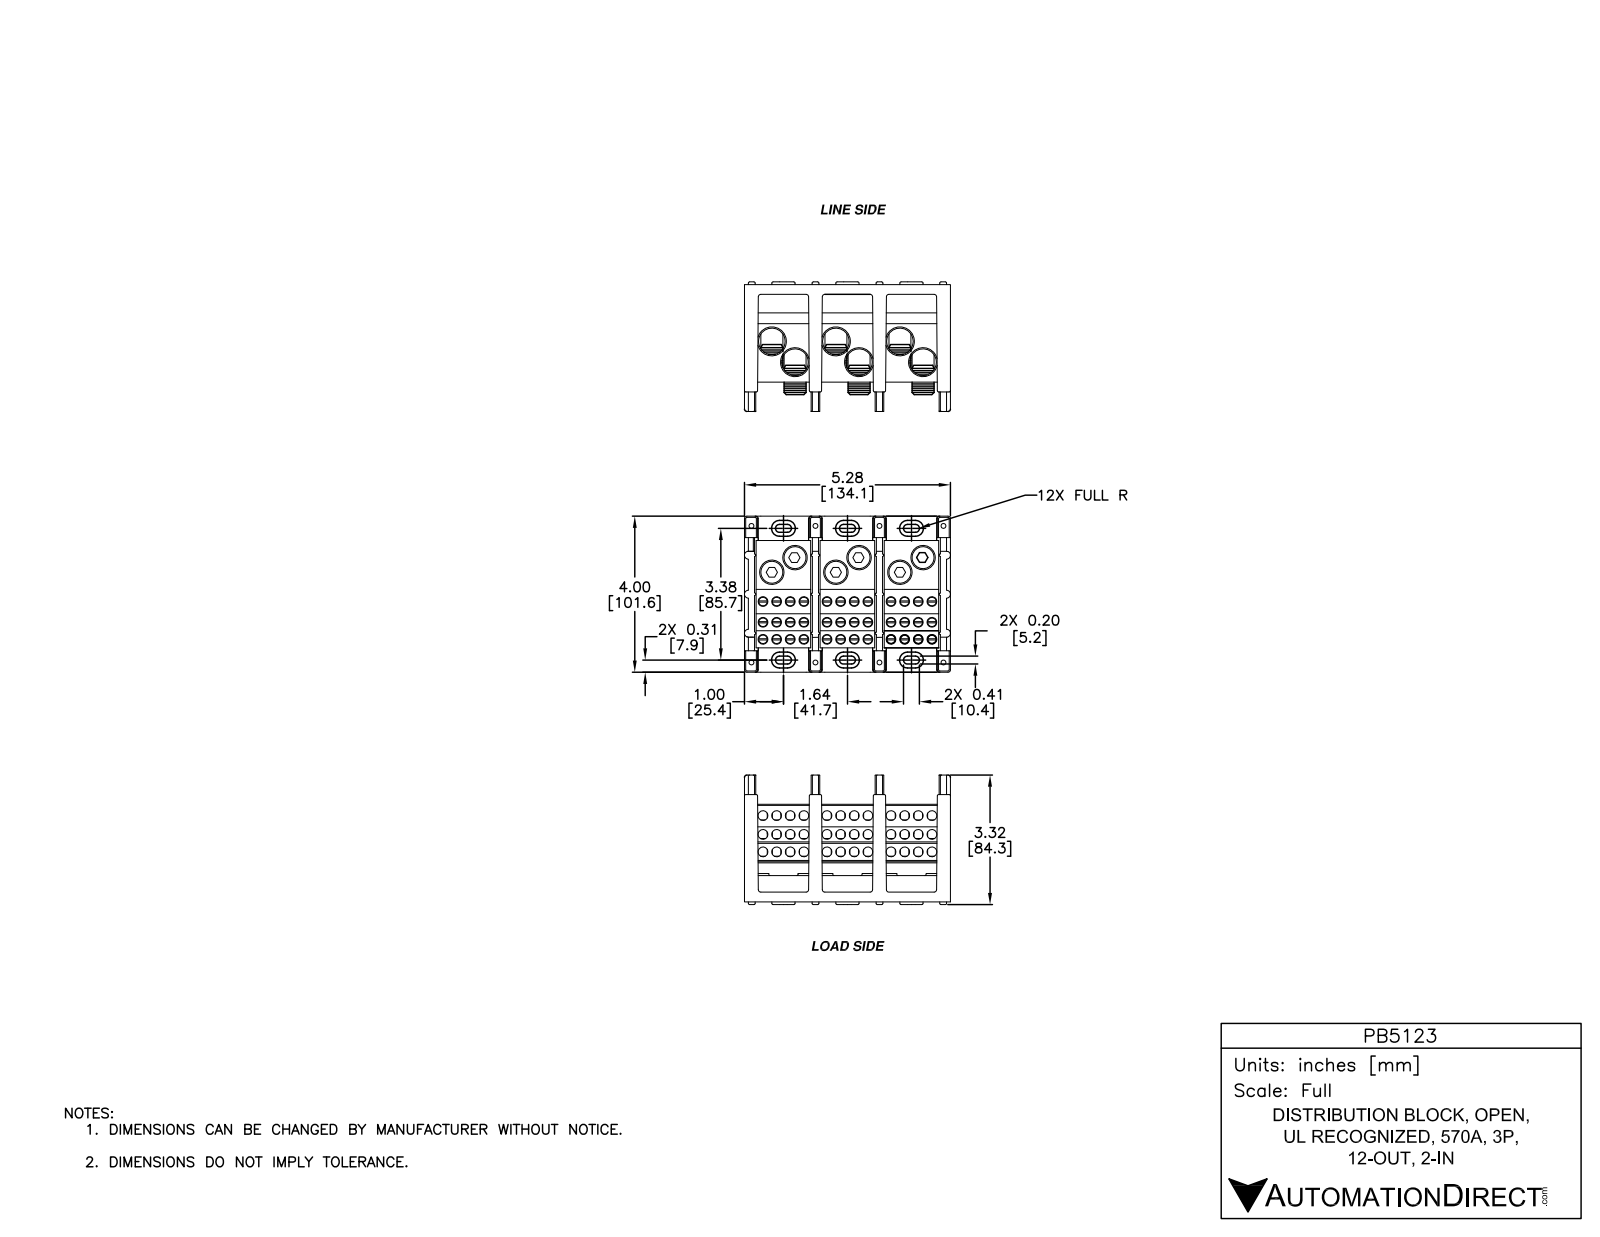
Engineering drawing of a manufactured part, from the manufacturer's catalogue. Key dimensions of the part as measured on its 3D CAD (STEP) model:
Part name (STEP PRODUCT): PB5123
STEP written by: SolidWorks 2014 (AUTOMOTIVE_DESIGN)
Units: inches
Bodies: 11 solids, 1869 faces (760 planar, 784 cylindrical, 325 other)
Overall size (bounding box): 5.281 × 4 × 3.35
Volume: 26.18 in³ · Surface area: 302.2 in²
Round holes (diameter × count): ⌀0.219 ×60, ⌀0.25 ×36, ⌀0.125 ×8, ⌀0.68 ×6, ⌀0.563 ×4, ⌀0.5 ×3, ⌀0.75 ×3
Round bosses / shafts (diameter × count): ⌀0.174 ×8, ⌀0.062 ×7, ⌀0.563 ×5, ⌀0.375 ×3
Partial cylindrical surfaces — rounded edges, fillets, slot ends (radius × count): R0.031 ×79, R0.1 ×54, R0.063 ×37, R0.203 ×28, R0.062 ×21, R0.094 ×12
Main face-to-face distances: 1.641, 3.281, 0.159, 1.481, 1.8, 0.1, 3.122, 0.75, 0.35, 3.441
Hole centre spacings: 0.349, 0.699, 0.636, 0.35, 0.993, 3.282, 2.933, 0.448
